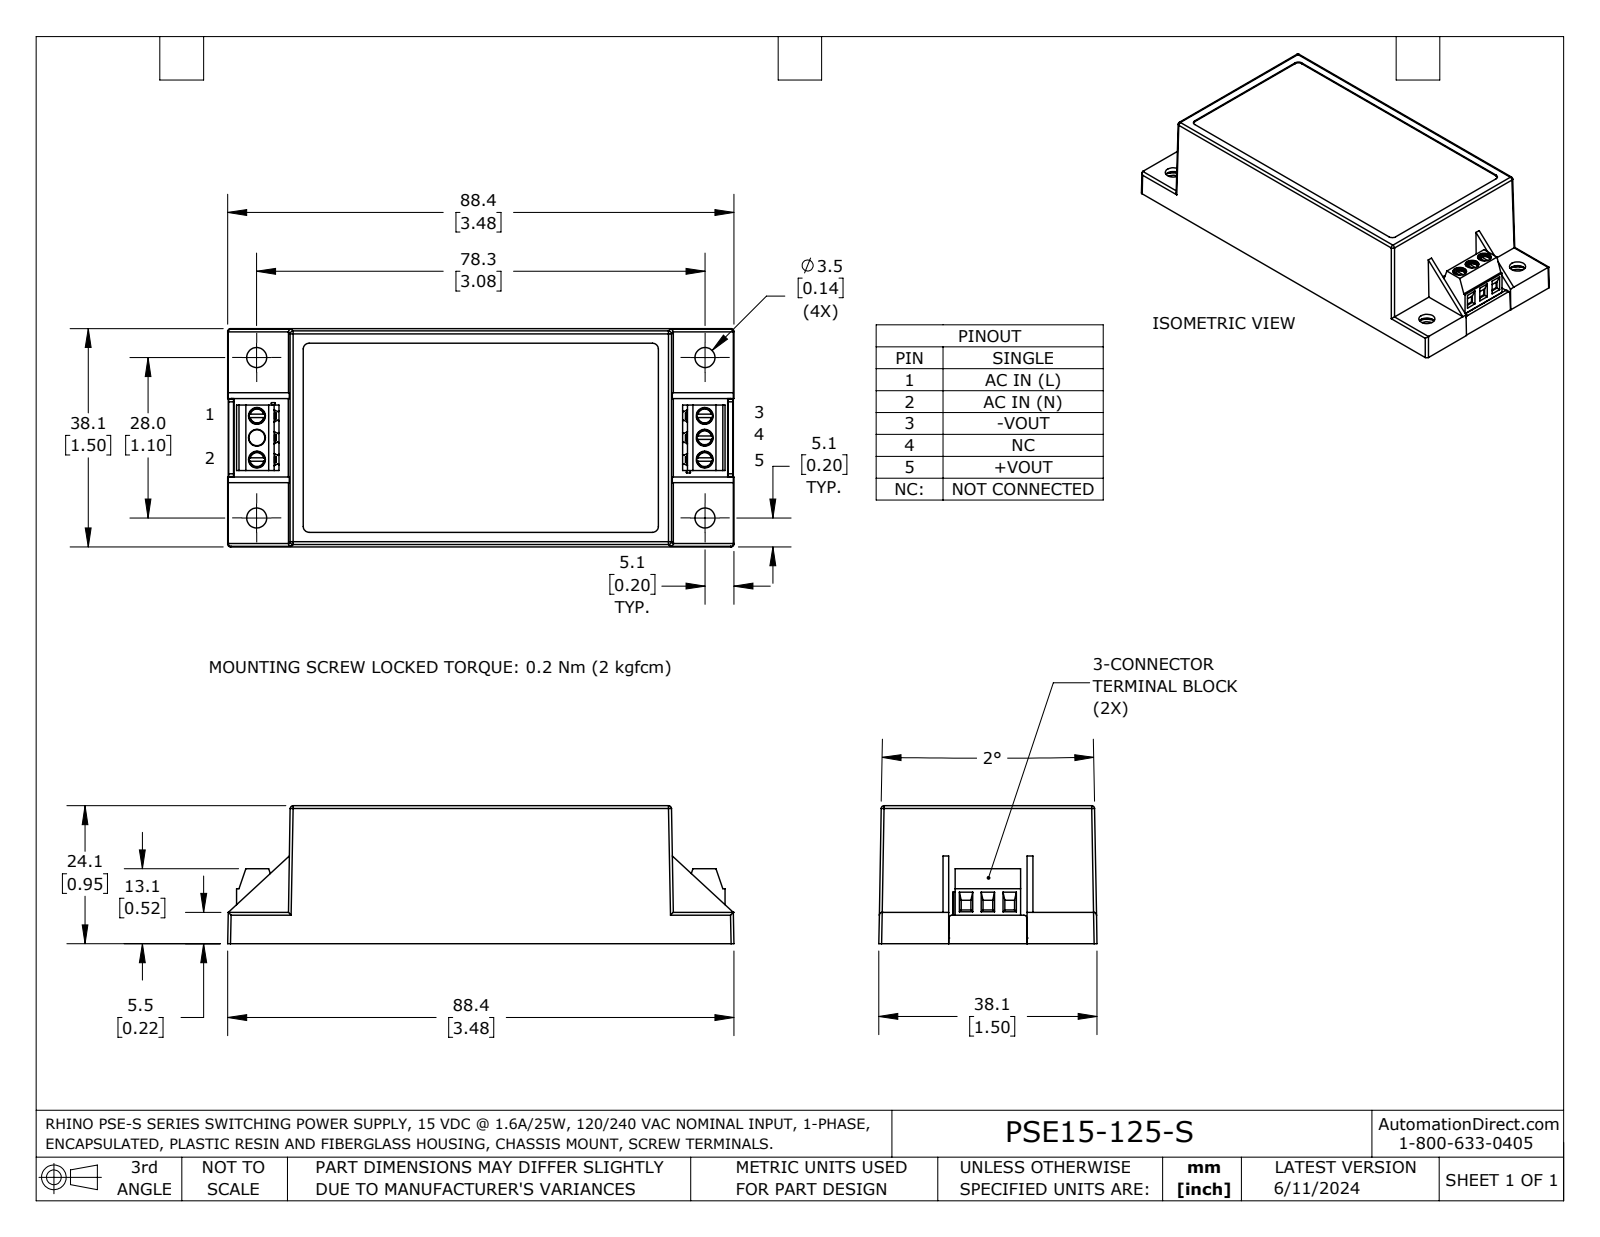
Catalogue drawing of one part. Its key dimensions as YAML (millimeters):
part_name: "PSE15-125-S"
step_written_by: "SolidWorks 2023 (AUTOMOTIVE_DESIGN)"
units: millimeters
bodies: {solids: 4, faces: 488, planar: 328, cylindrical: 126, other: 34}
overall_size: [88.4, 38.1, 24.1]
volume: 11600
surface_area: 24830
round_holes:
  - {diameter: 2.9, count: 6}
  - {diameter: 3.5, count: 4}
  - {diameter: 2.8, count: 1}
partial_cylinders:
  - {radius: 0.2, count: 18}
  - {radius: 0.5, count: 18}
  - {radius: 0.2, count: 12}
  - {radius: 0.1, count: 8}
  - {radius: 0.2, count: 4}
  - {radius: 0.3, count: 4}
  - {radius: 1, count: 4}
  - {radius: 2, count: 4}
face_to_face_distances: [1, 22.9, 21.9, 23.9, 36.1, 4.5, 18.4, 65.4, 3.5, 19.4]
hole_center_spacings: [3.8, 78.3, 78.2, 7.6, 10.2, 10.2, 14, 14]
